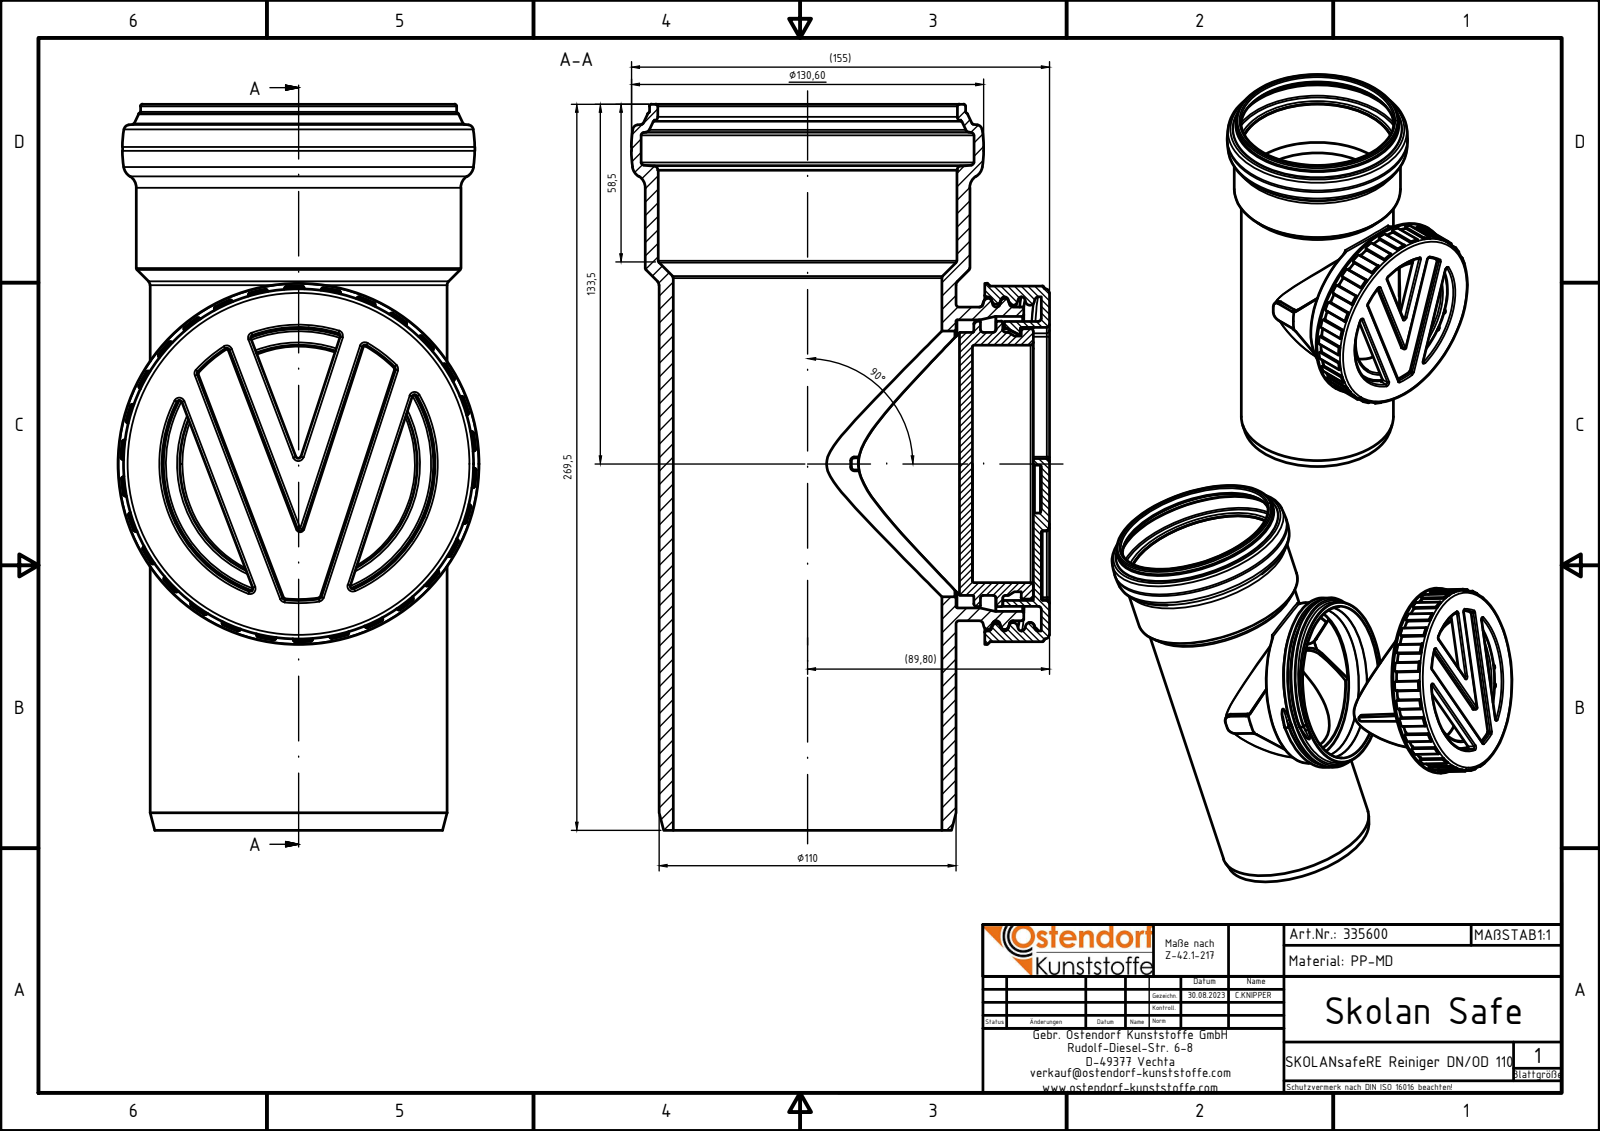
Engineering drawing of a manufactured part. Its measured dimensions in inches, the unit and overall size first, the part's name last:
Units: inches
Overall size (bounding box): 10.61 × 6.11 × 5.276
Round holes (diameter × count): ⌀3.469 ×1, ⌀3.886 ×1, ⌀3.925 ×1, ⌀3.992 ×1, ⌀4.209 ×1, ⌀4.311 ×1, ⌀4.366 ×1, ⌀4.378 ×1, ⌀4.866 ×1, ⌀4.882 ×1
Round bosses / shafts (diameter × count): ⌀5.276 ×1, ⌀5.15 ×1, ⌀5.118 ×1, ⌀4.744 ×1, ⌀4.622 ×1, ⌀4.587 ×1, ⌀4.343 ×1, ⌀4.169 ×1
Partial cylindrical surfaces — rounded edges, fillets, slot ends (radius × count): R0.024 ×127, R0.012 ×72, R0.039 ×30, R0.02 ×23, R0.016 ×6, R0.047 ×6, R0.079 ×6, R0.059 ×4
Main face-to-face distances: 0.118, 0.236, 0.098, 0.709, 0.827, 0.945, 0.327, 0.681, 0.445, 0.264
Volume: 41.82 in³ · Surface area: 479.4 in²
Bodies: 3 solids, 1190 faces (183 planar, 362 cylindrical, 645 other)
Part name (STEP PRODUCT): Zusammenbau Reiniger DN110; 335600 Skolan Safe-RE Reiniger DN_OD 110; Einsatz und Deckel; 335600_1 Innteil für Reiniger DN_OD 110 (+1 more)
STEP written by: Autodesk Inventor 2024 (AUTOMOTIVE_DESIGN)
